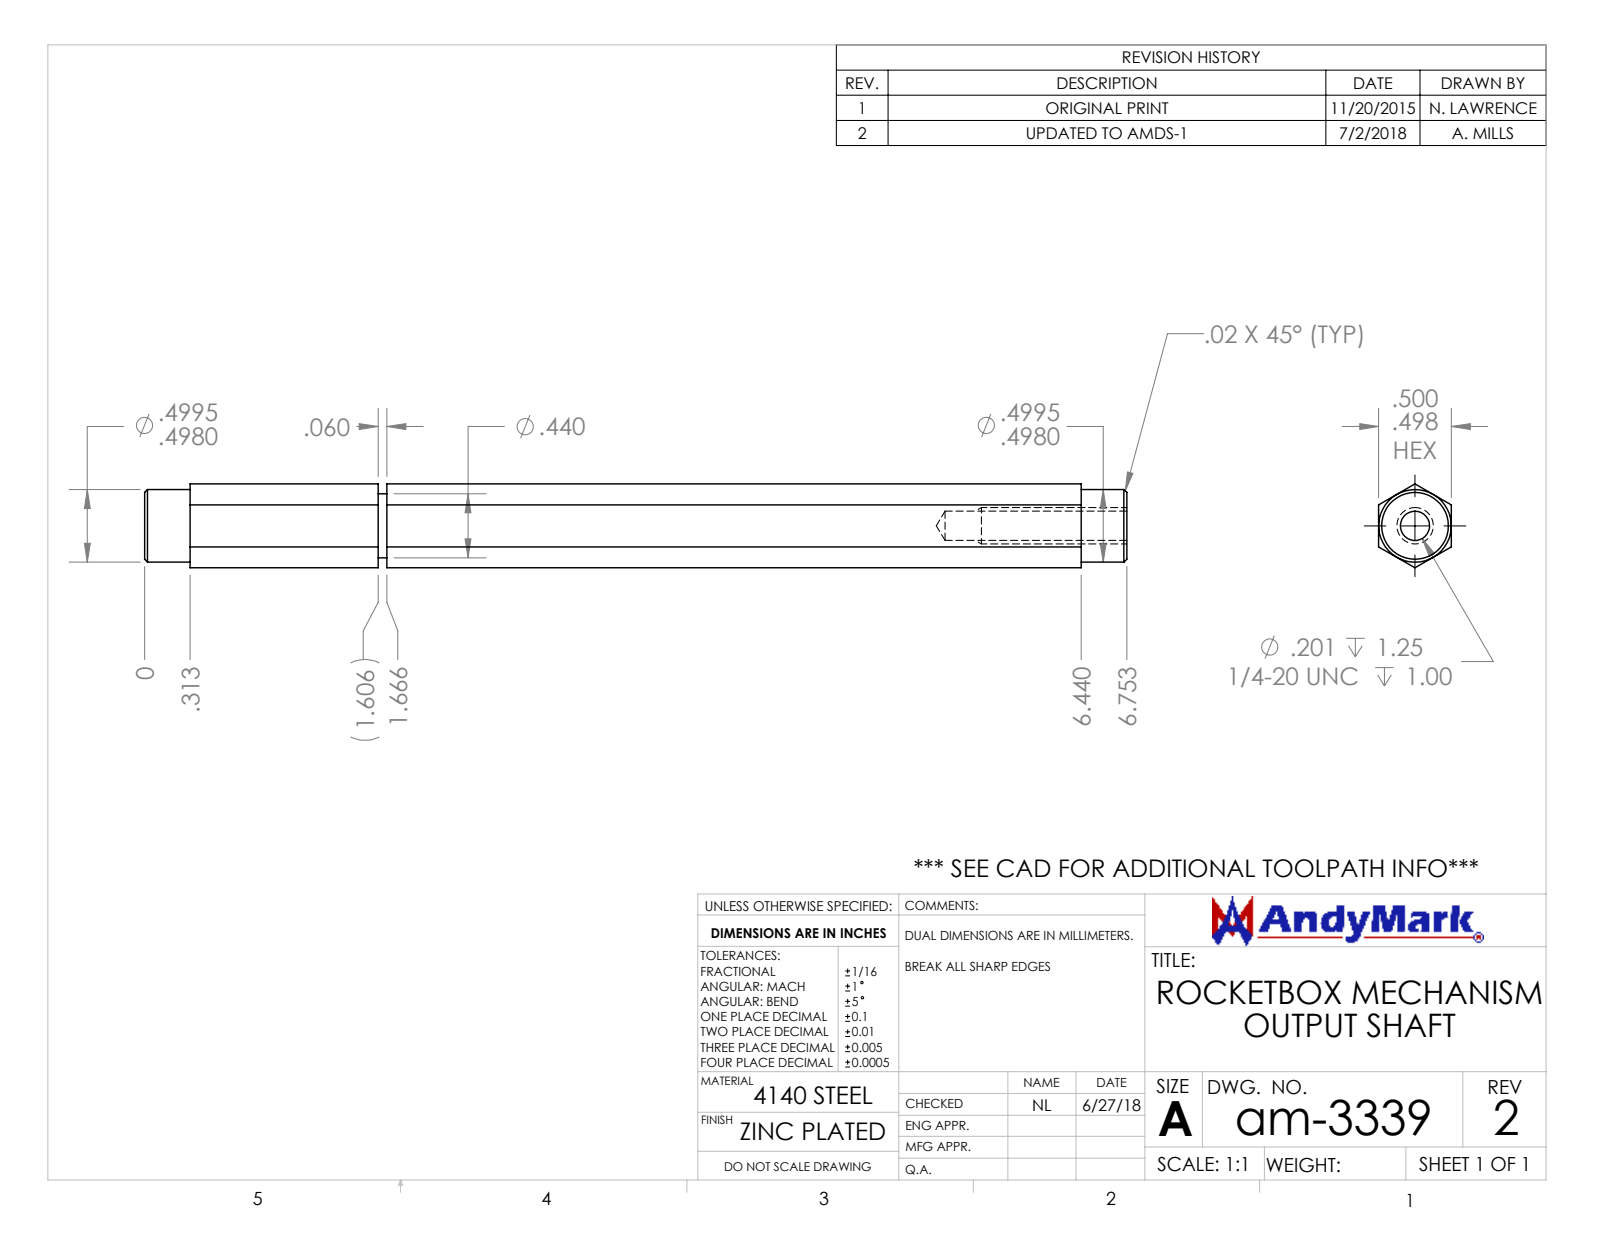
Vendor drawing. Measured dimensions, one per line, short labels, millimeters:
name: am-3339 PTO Mechanism Shaft
written by: SolidWorks 2017 (AUTOMOTIVE_DESIGN)
unit: mm
bodies: 1 solid, 32 faces (18 planar, 8 cylindrical, 6 other)
size: 171.5 × 14.7 × 12.7
volume: 23 010 mm³; area: 8 316 mm²
holes: 1× ⌀5.1
bosses: 1× ⌀12.7, 1× ⌀11.2
face distances: 12.7, 171.5, 40.8, 130.7, 42.3, 1.5, 129.2, 8, 163.6, 32.8
